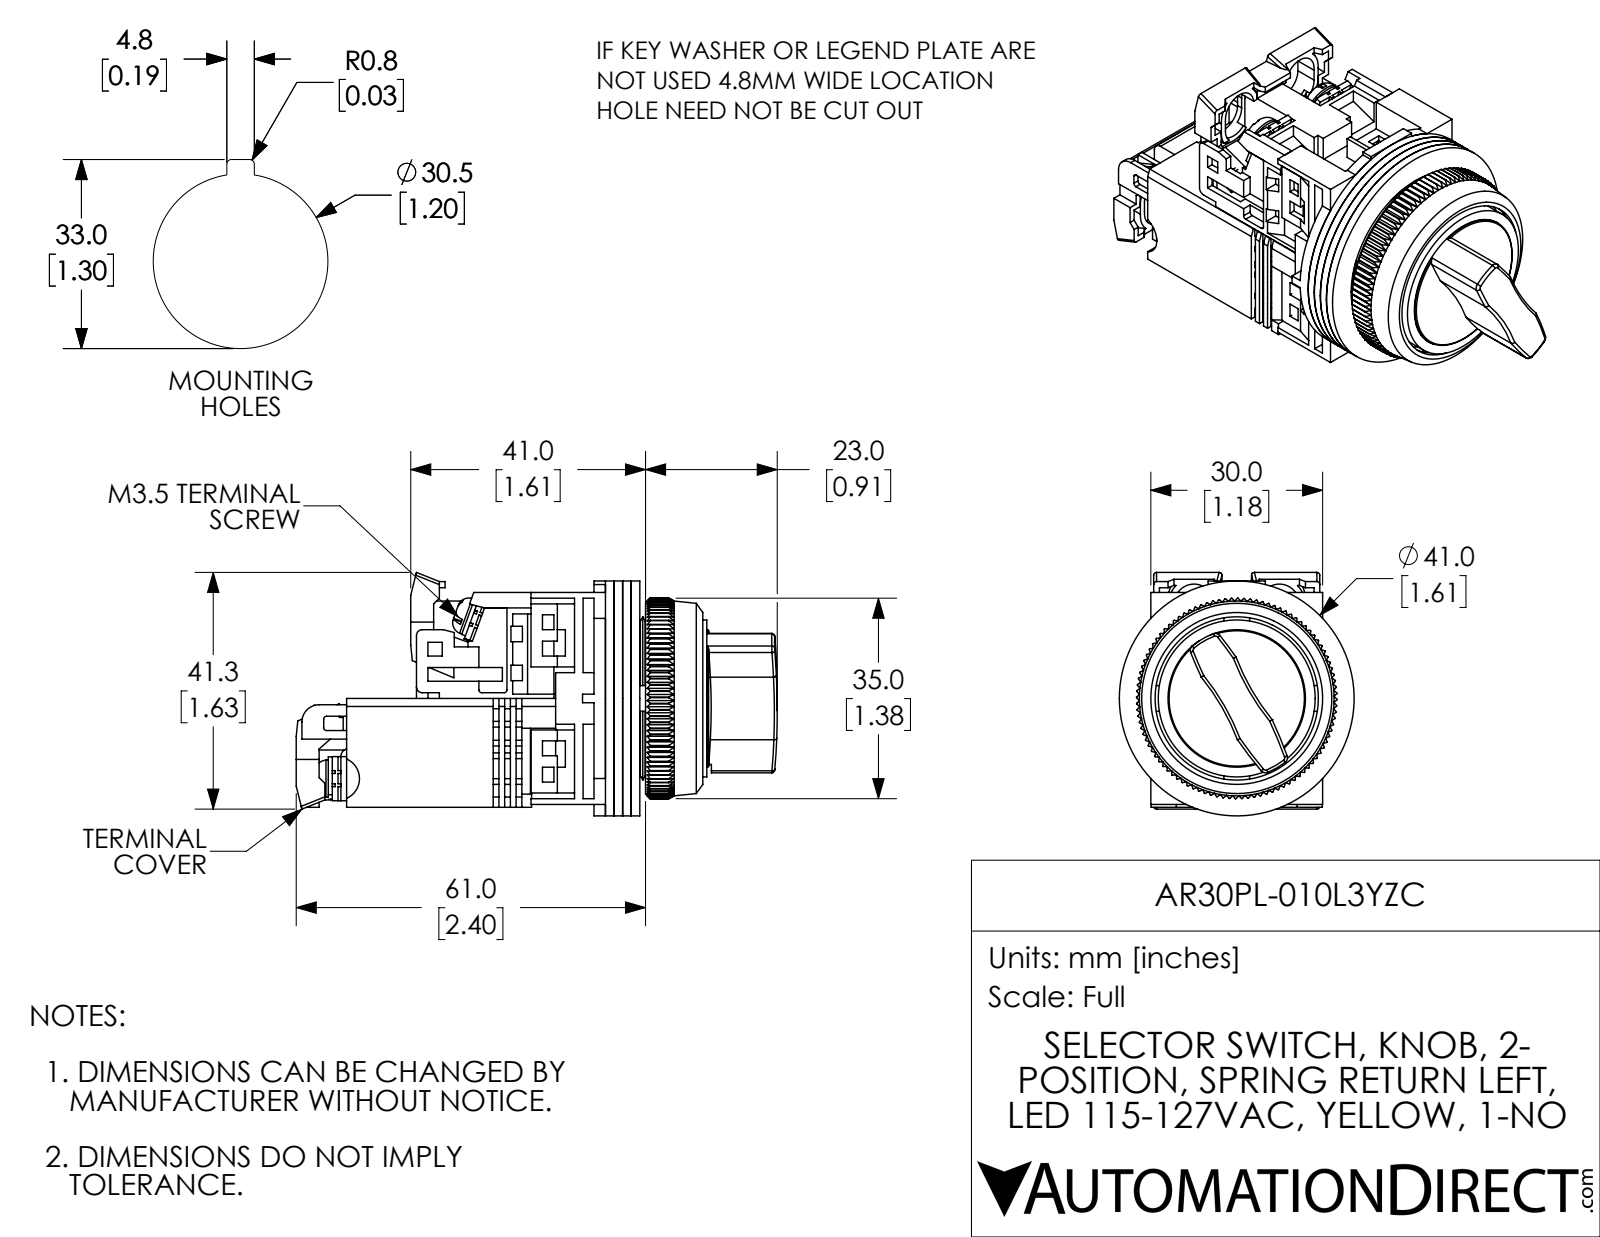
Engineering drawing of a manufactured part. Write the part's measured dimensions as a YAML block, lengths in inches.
part_name: "AR30PL-010L3YZC"
step_written_by: "SolidWorks 2017 (AUTOMOTIVE_DESIGN)"
units: inches
bodies: {solids: 27, faces: 2357, planar: 1706, cylindrical: 321, other: 330}
overall_size: [3.307, 1.673, 1.614]
volume: 3.001
surface_area: 63.38
round_holes:
  - {diameter: 0.138, count: 6}
  - {diameter: 0.142, count: 4}
  - {diameter: 0.118, count: 3}
  - {diameter: 0.472, count: 1}
  - {diameter: 0.709, count: 1}
  - {diameter: 0.768, count: 1}
  - {diameter: 0.827, count: 1}
  - {diameter: 1.122, count: 1}
  - {diameter: 1.181, count: 1}
  - {diameter: 1.252, count: 1}
round_bosses_or_shafts:
  - {diameter: 0.26, count: 4}
  - {diameter: 0.138, count: 2}
  - {diameter: 0.063, count: 2}
  - {diameter: 1.614, count: 1}
  - {diameter: 1.15, count: 1}
  - {diameter: 1.079, count: 1}
  - {diameter: 0.945, count: 1}
  - {diameter: 0.886, count: 1}
partial_cylinders:
  - {radius: 0.059, count: 17}
  - {radius: 0.02, count: 13}
  - {radius: 0.039, count: 6}
  - {radius: 0.138, count: 4}
  - {radius: 0.177, count: 4}
  - {radius: 0.118, count: 2}
  - {radius: 1.575, count: 2}
  - {radius: 2.953, count: 2}
face_to_face_distances: [0.059, 0.118, 0.177, 0.079, 0.039, 0.748, 0.787, 0.197, 0.256, 1.417]
hole_center_spacings: [0.579, 0.297, 0.624, 0.02, 0.302, 0.583, 0.583, 0.606]
